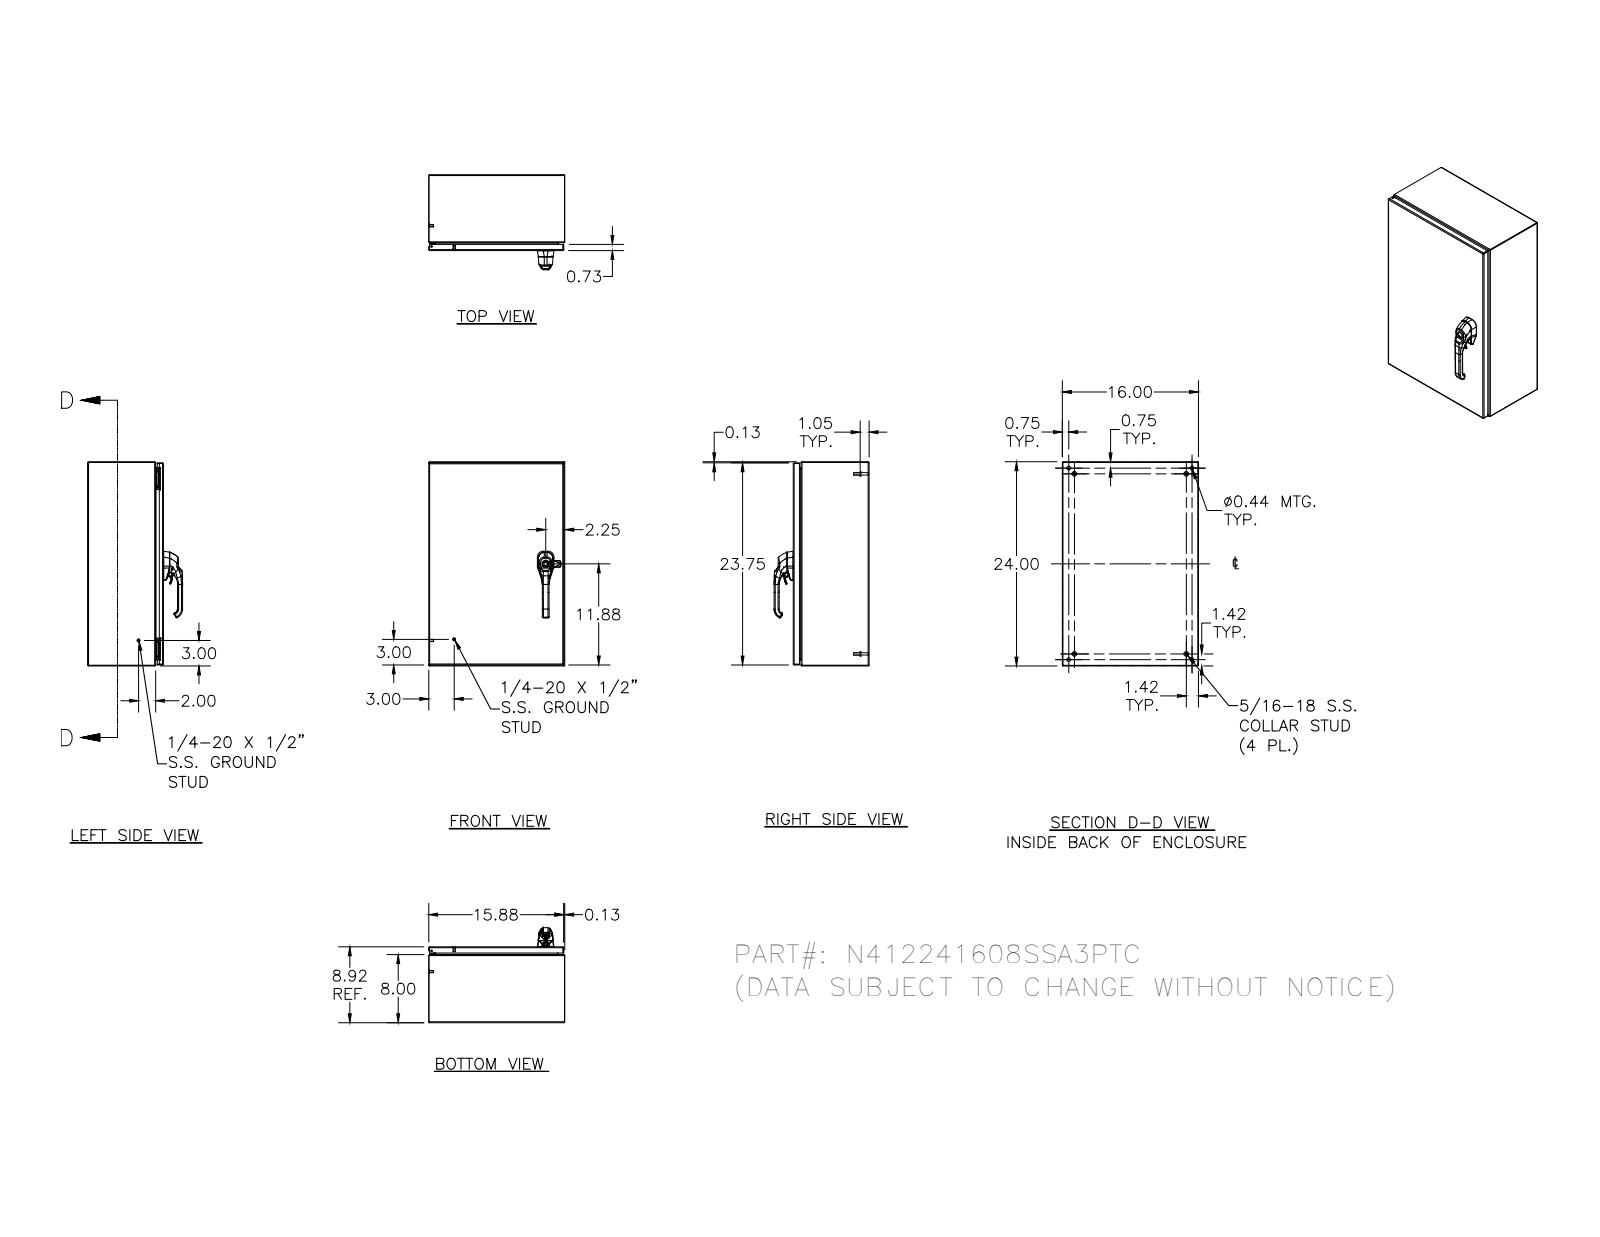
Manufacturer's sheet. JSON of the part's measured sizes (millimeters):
{"part_name": "N412241608SSA3PTC; N412241608SSA3PTCBKP; N4122416SSA3PTCLID; HFW328176 (+8 more)", "step_written_by": "Autodesk Inventor 2011 (AUTOMOTIVE_DESIGN)", "units": "millimeters", "bodies": {"solids": 41, "faces": 2769, "planar": 882, "cylindrical": 1022, "other": 865}, "overall_size": [609.6, 406.4, 283.6], "volume_mm3": 2019000, "surface_area_mm2": 2096000, "round_holes": [[4.8, 5], [2.4, 4], [3.9, 4], [4.2, 4], [4.4, 4], [11.1, 4], [5.4, 3], [4, 2], [8, 2], [10.2, 2], [10.5, 2], [3.1, 1]], "round_bosses_or_shafts": [[6.4, 10], [14.3, 4], [9.1, 4], [8.1, 4], [7.6, 4], [7, 4], [6.5, 4], [4.2, 4]], "partial_cylinders_radius": [[0.5, 173], [0.3, 101], [0.8, 30], [1.3, 26], [0.5, 21], [2.7, 20], [0.4, 18], [2, 14]], "face_to_face_distances": [1.9, 224.6, 404.5, 226.5, 222.7, 607.7, 402.6, 406.4, 609.6, 605.8], "hole_center_spacings": [507.9, 0.4, 16.8, 524.7, 0.5, 12.7, 16.5, 16.7]}
